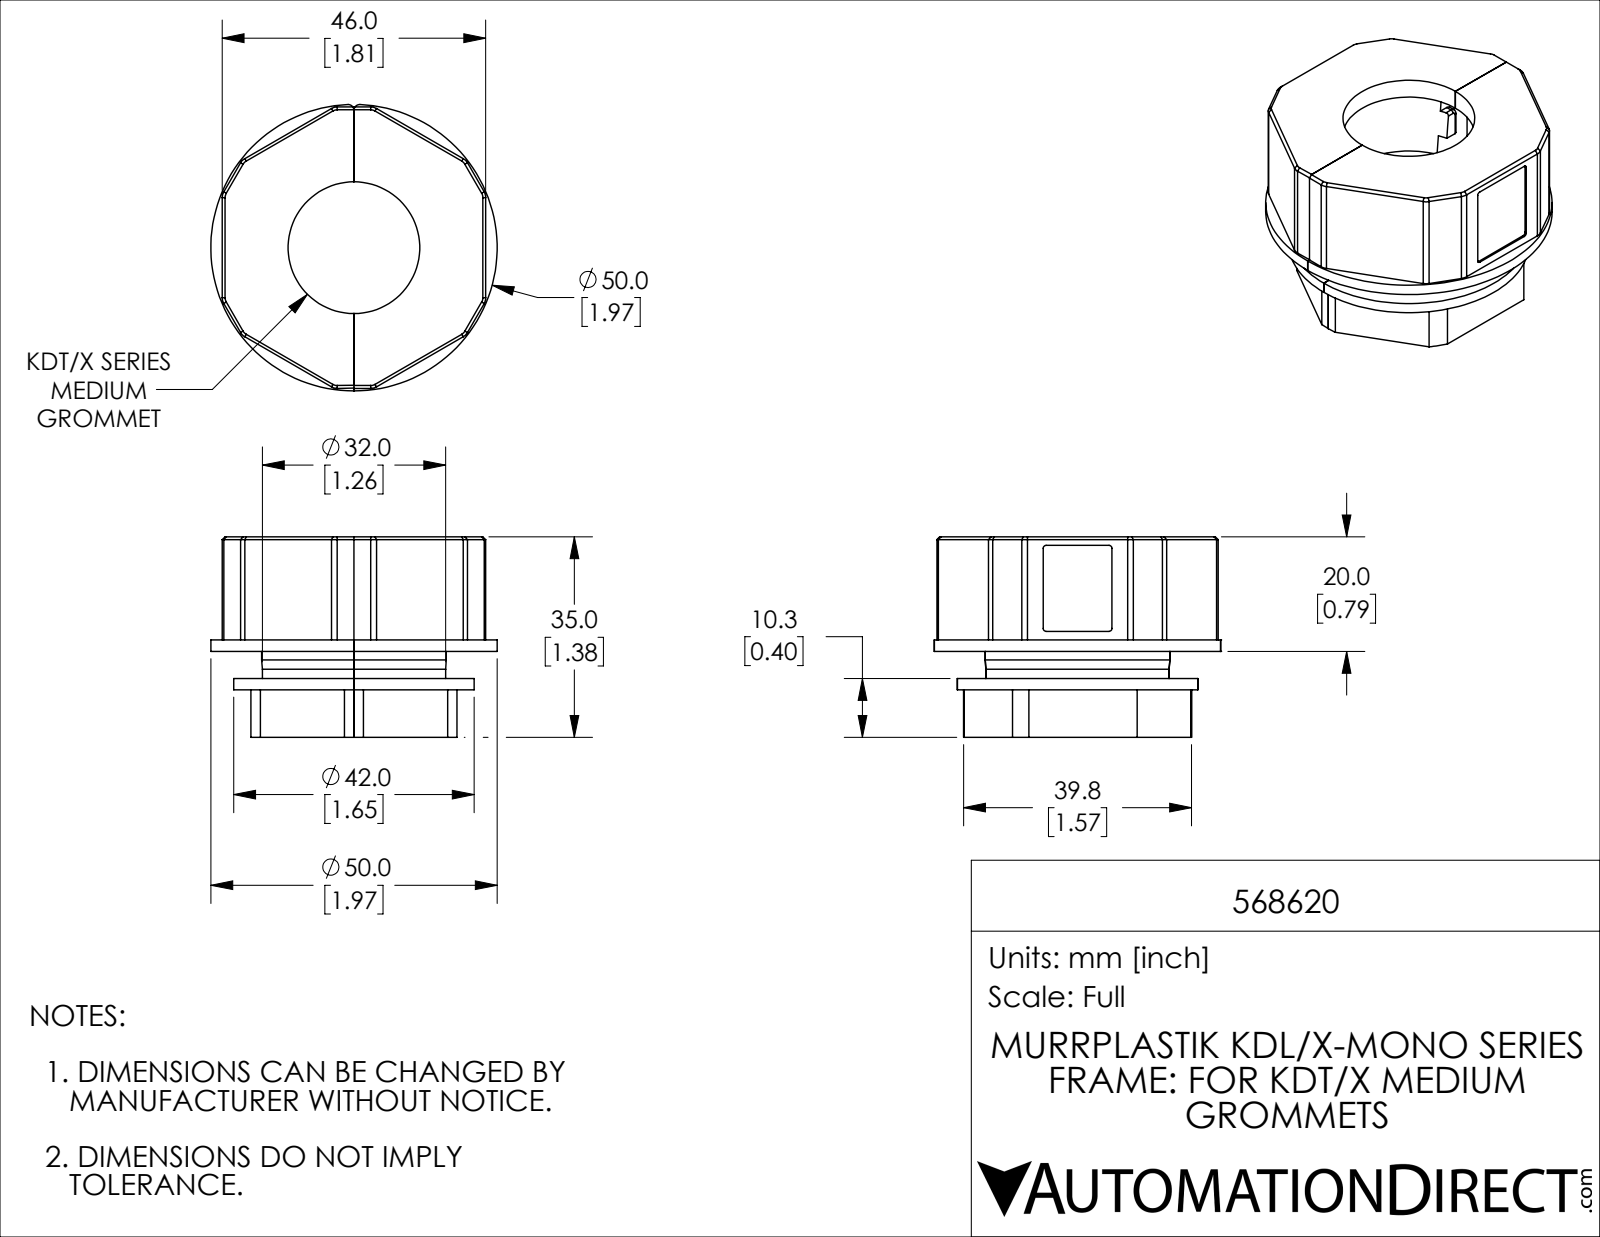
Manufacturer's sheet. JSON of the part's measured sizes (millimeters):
{"part_name": "568620", "step_written_by": "SolidWorks 2019 (CONFIG_CONTROL_DESIGN)", "units": "millimeters", "bodies": {"solids": 2, "faces": 169, "planar": 66, "cylindrical": 70, "other": 33}, "overall_size": [50, 49.98, 35], "volume_mm3": 29918, "surface_area_mm2": 11772, "round_holes": [[23, 1], [25, 1]], "round_bosses_or_shafts": [[50, 1], [32.25, 1], [32, 1]], "partial_cylinders_radius": [[2, 12], [0.5, 8], [1, 3]], "face_to_face_distances": [20, 46, 22.7, 49.12, 23, 45.7, 15, 16.4, 3.6, 31.4]}
